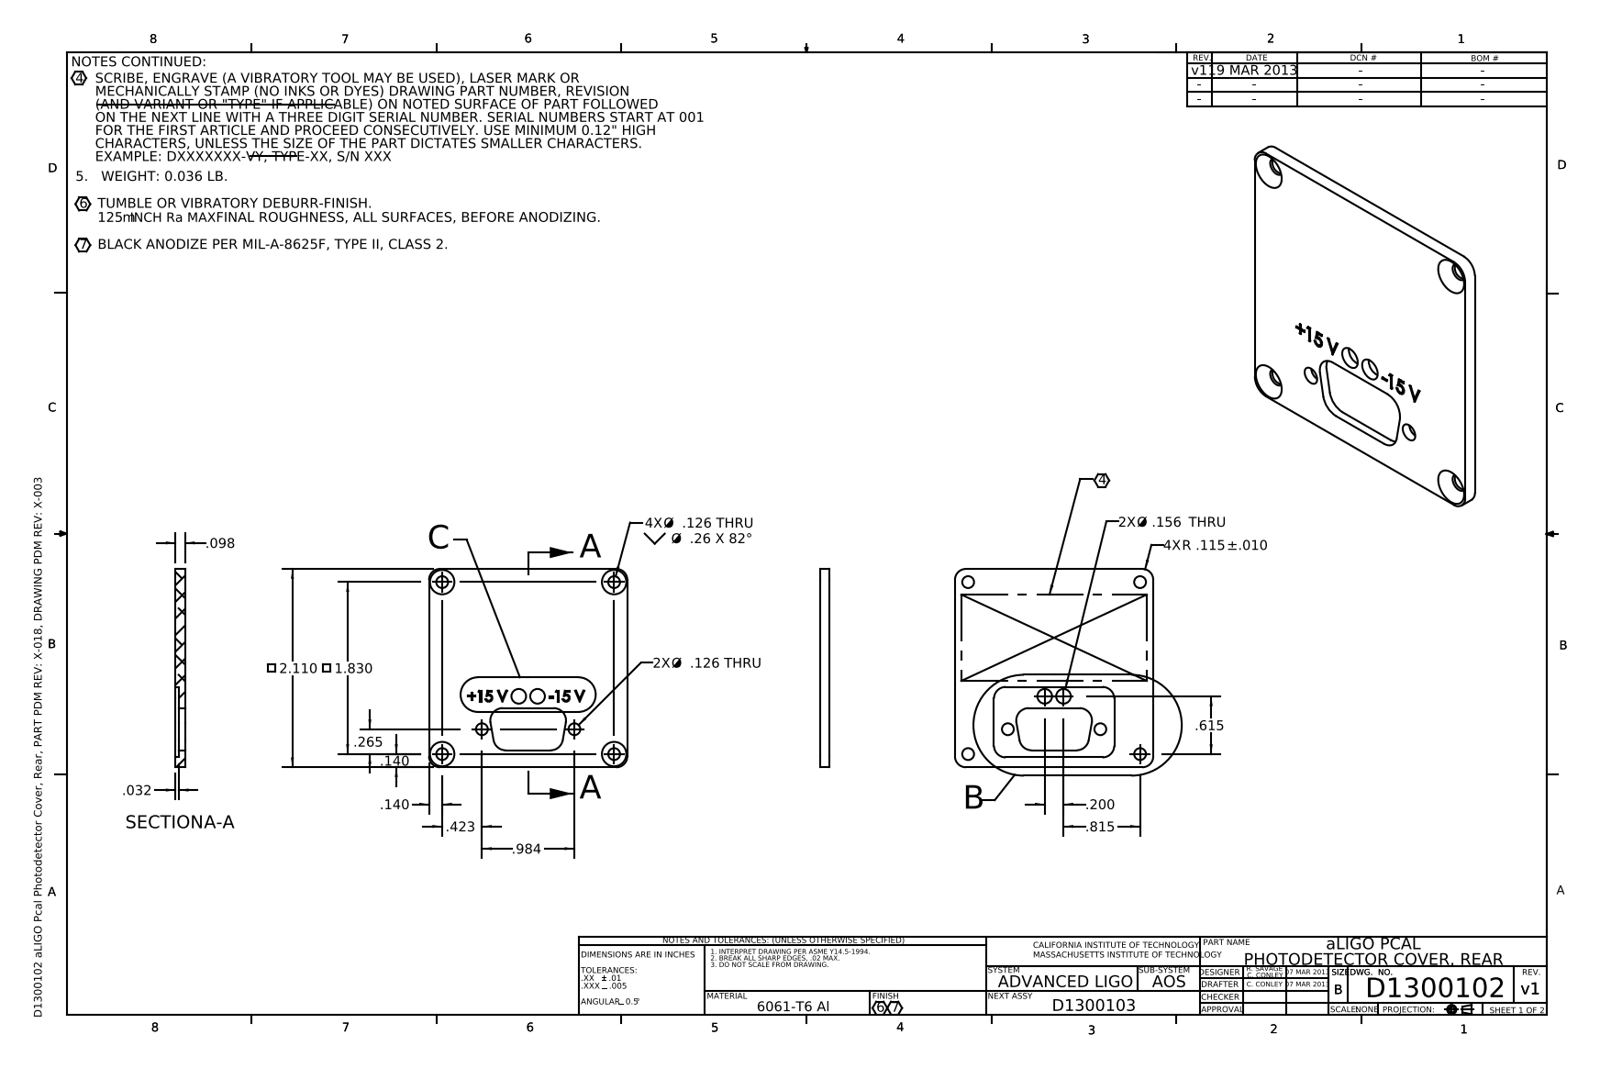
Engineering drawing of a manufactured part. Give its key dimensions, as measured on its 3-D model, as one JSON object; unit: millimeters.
{"part_name": "D1300102-v1 aLIGO Pcal Photodetector Cover, Rear", "step_written_by": "SolidWorks 2013 (AUTOMOTIVE_DESIGN)", "units": "millimeters", "bodies": {"solids": 1, "faces": 130, "planar": 77, "cylindrical": 29, "other": 24}, "overall_size": [53.6, 53.6, 2.5], "volume_mm3": 6060, "surface_area_mm2": 6034, "round_holes": [[3.2, 6], [4, 2]], "partial_cylinders_radius": [[2.9, 4], [3.2, 4], [3.4, 4]], "face_to_face_distances": [2.5, 0.8, 1.7, 53.6, 16, 37.6, 2.7, 19.1, 13.3, 51], "hole_center_spacings": [46.5, 12.7, 13.4, 17.5, 25.9, 30.1, 36.4, 37.2]}
